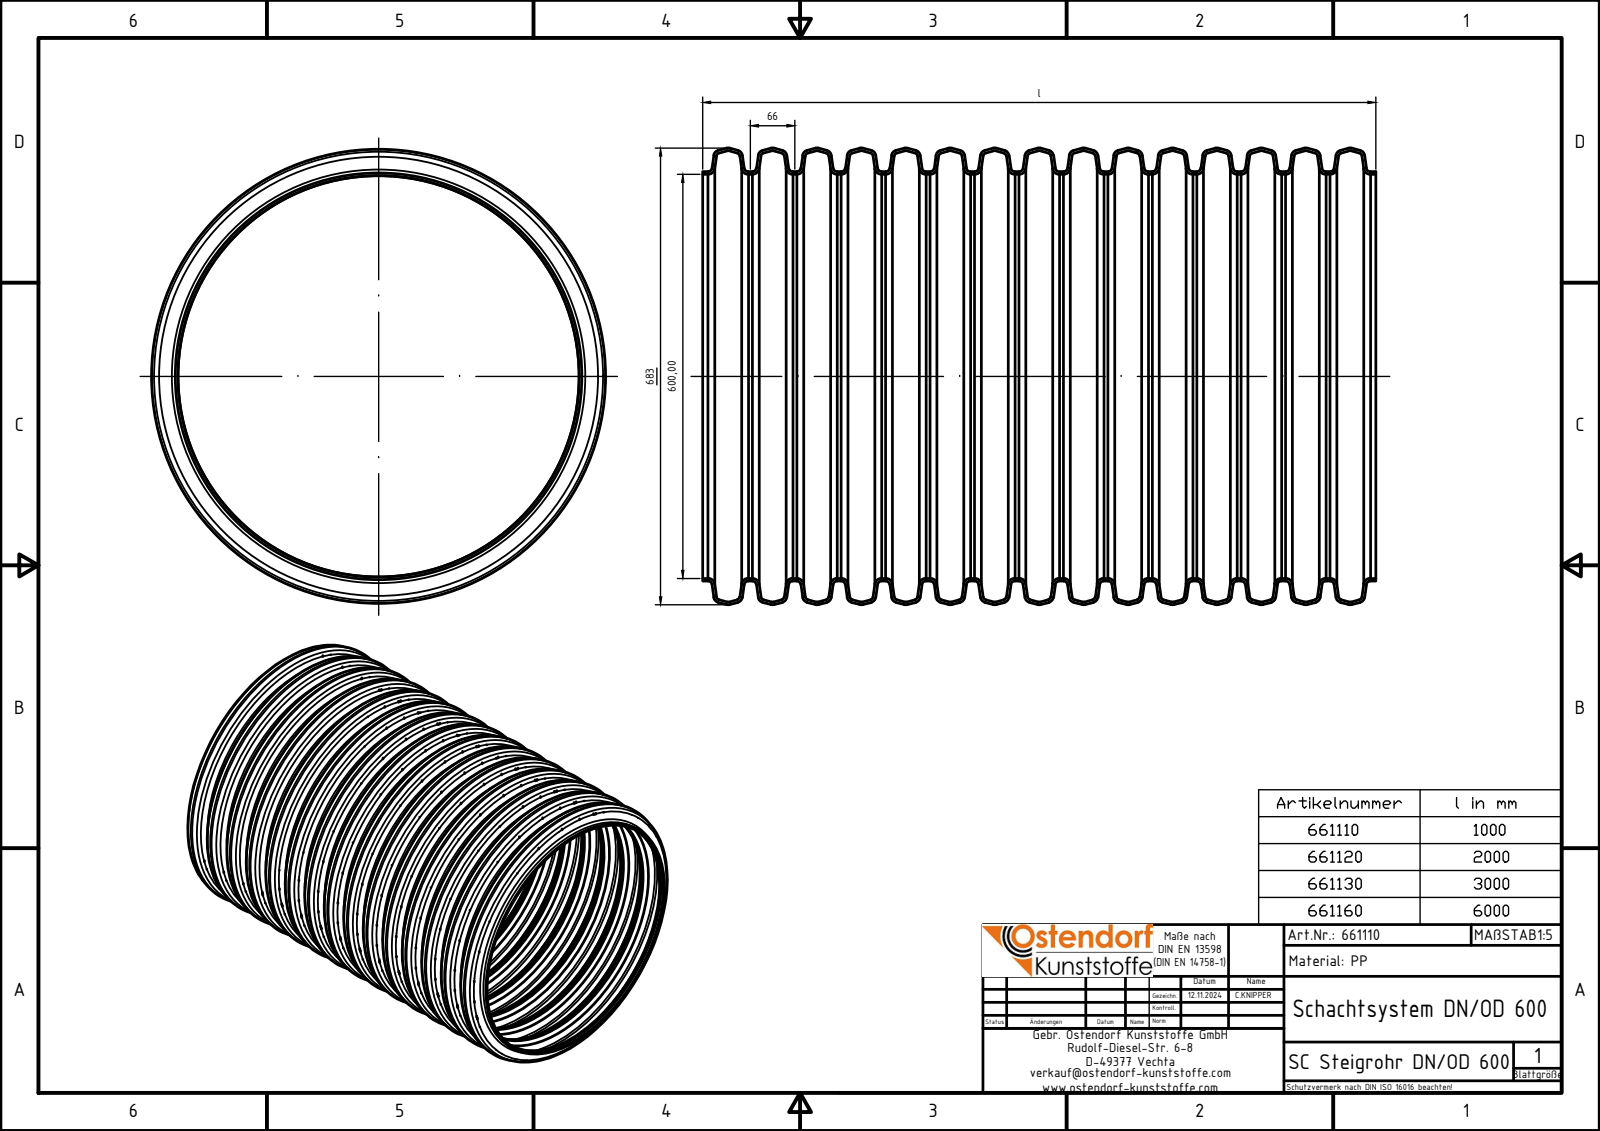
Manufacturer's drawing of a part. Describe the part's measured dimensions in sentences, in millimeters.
The part is named "661110z". Its 3-D file was written by "Autodesk Inventor 2024 (AUTOMOTIVE_DESIGN)". It is 1 solid with 304 faces: 2 planar, 32 cylindrical and 270 other. Overall it measures 1000 by 678.36 by 678.36 millimeters. Its volume is 13 770 000 cubic millimeters and its surface area 6 893 000 square millimeters. Round holes: 1 of diameter 600. Round bosses or shafts: 1 of diameter 607.99. The main face-to-face distances are 1000.
